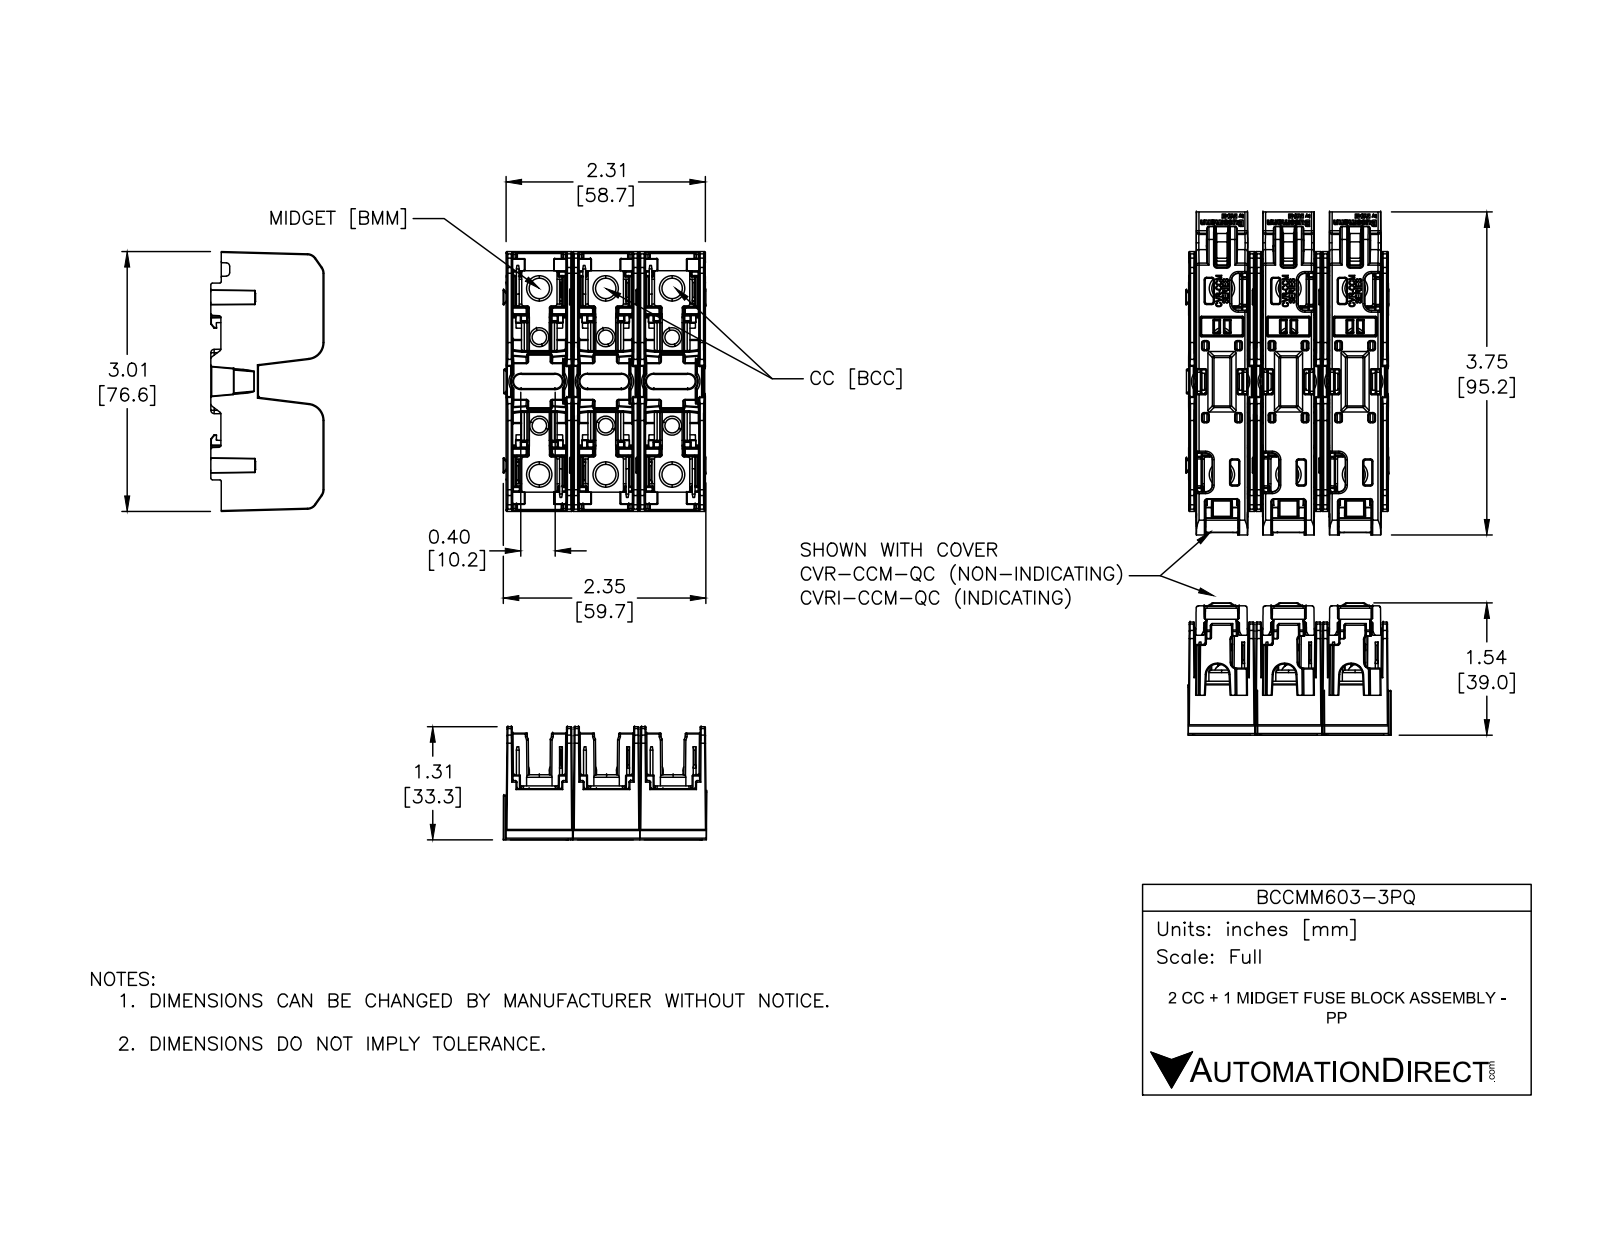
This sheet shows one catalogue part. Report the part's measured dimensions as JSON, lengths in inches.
{"part_name": "BCCMM603-3PQ", "step_written_by": "SolidWorks 2021 (CONFIG_CONTROL_DESIGN)", "units": "inches", "bodies": {"solids": 13, "faces": 1461, "planar": 1026, "cylindrical": 277, "other": 158}, "overall_size": [3.015, 2.346, 1.312], "volume_in3": 3.718, "surface_area_in2": 77.69, "round_holes": [[0.142, 6], [0.075, 4]], "round_bosses_or_shafts": [[0.295, 6], [0.22, 4], [0.138, 4]], "partial_cylinders_radius": [[0.004, 36], [0.02, 36], [0.03, 6], [0.053, 6], [0.061, 6], [0.084, 6], [0.085, 6], [0.175, 6]], "face_to_face_distances": [0.768, 1.535, 0.691, 0.691, 0.594, 0.077, 0.077, 1.458, 1.459, 0.032], "hole_center_spacings": [0.768, 1.281, 1.025, 0.119, 1.535, 1.846, 2.232, 2.124]}
